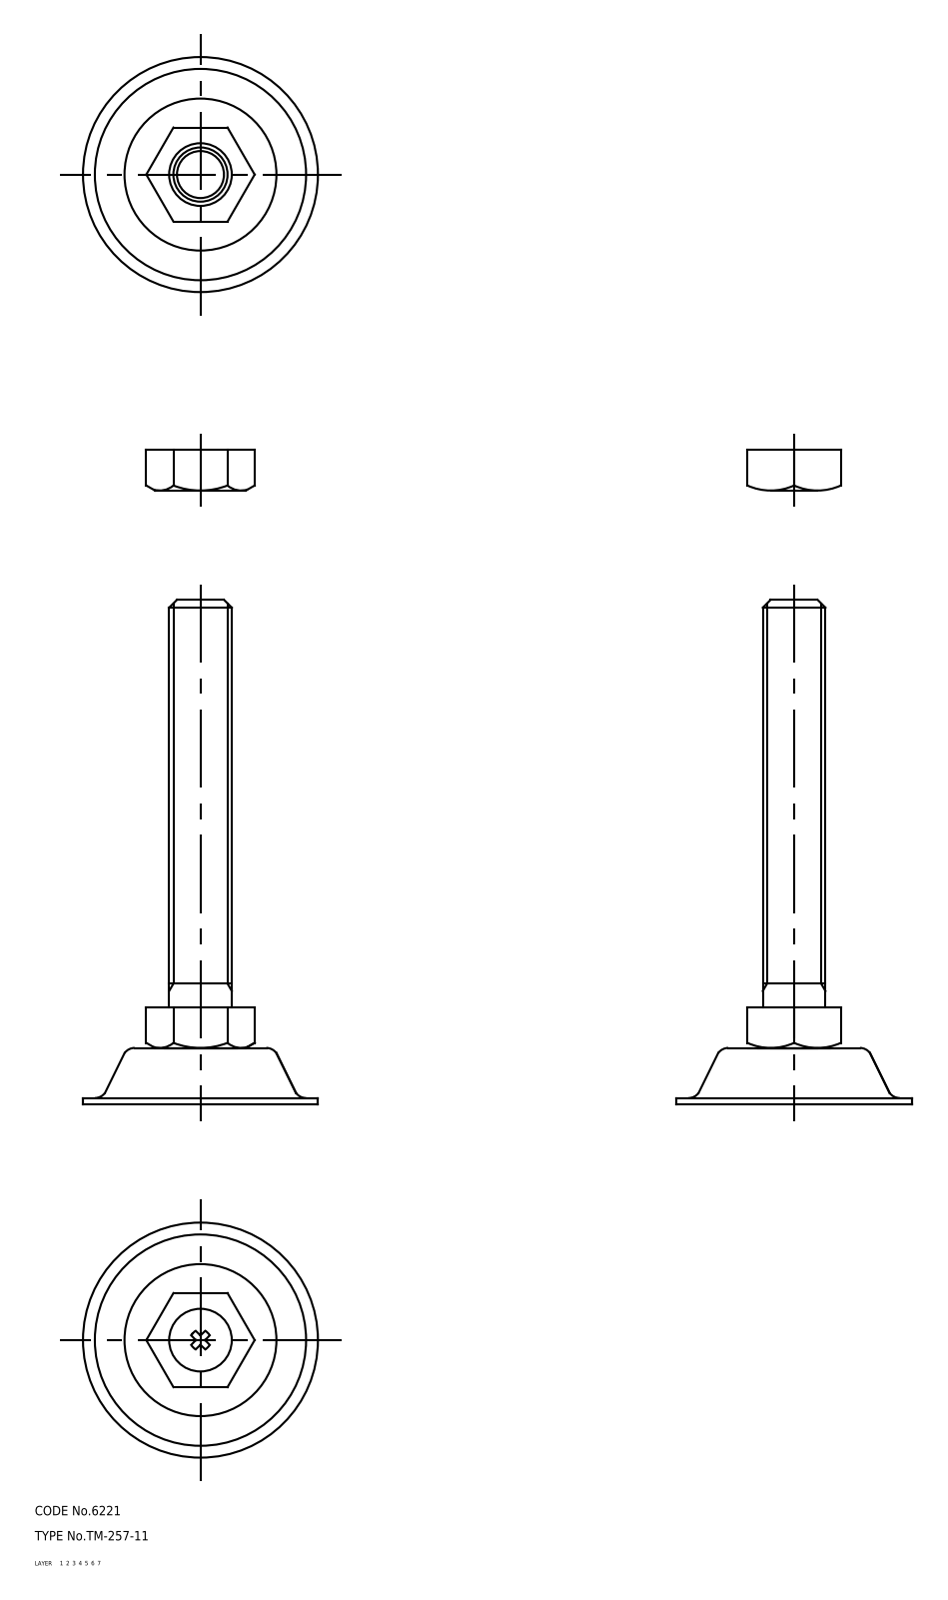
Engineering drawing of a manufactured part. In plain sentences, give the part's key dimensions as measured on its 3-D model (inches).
The part is named "nut; foot; bolt; TM_257_11_9541_36". Its 3-D file was written by "CADfix (AUTOMOTIVE_DESIGN)". It is 4 solids with 83 faces: 0 planar, 0 cylindrical and 83 other. Overall it measures 6.339 by 2.953 by 2.953 inches. Its volume is 4.819 cubic inches and its surface area 46.38 square inches.
